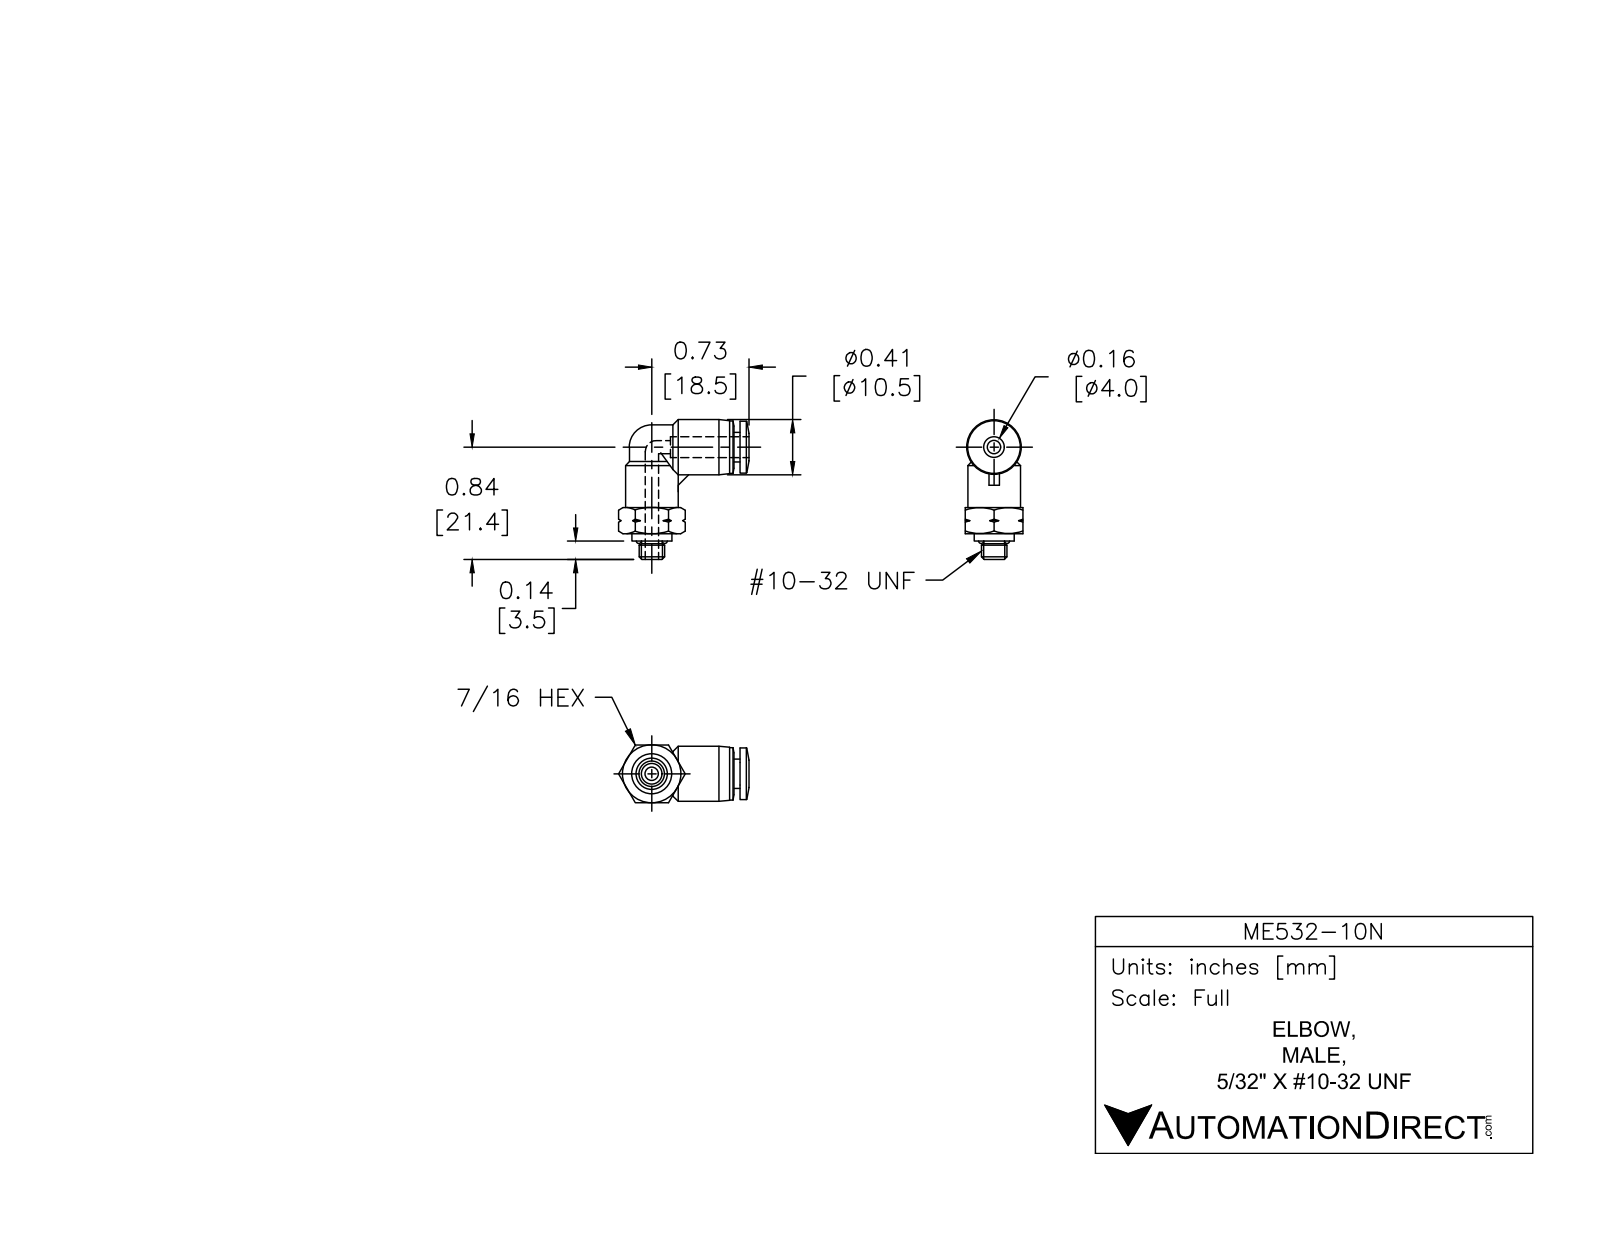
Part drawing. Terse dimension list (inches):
name: ME532-10N
written by: SolidWorks 2015 (AUTOMOTIVE_DESIGN)
unit: in
bodies: 2 solids, 105 faces (18 planar, 29 cylindrical, 58 other)
size: 1.049 × 0.978 × 0.433
volume: 0.151 in³; area: 2.982 in²
holes: 2× ⌀0.098, 1× ⌀0.156, 1× ⌀0.169
bosses: 2× ⌀0.394, 1× ⌀0.413, 1× ⌀0.388, 1× ⌀0.299, 1× ⌀0.22, 1× ⌀0.19
rounds: 2× R0.167
face distances: 0.433, 0.045, 0.197, 0.024, 0.22, 0.47, 0.516, 0.031, 0.055, 0.252
